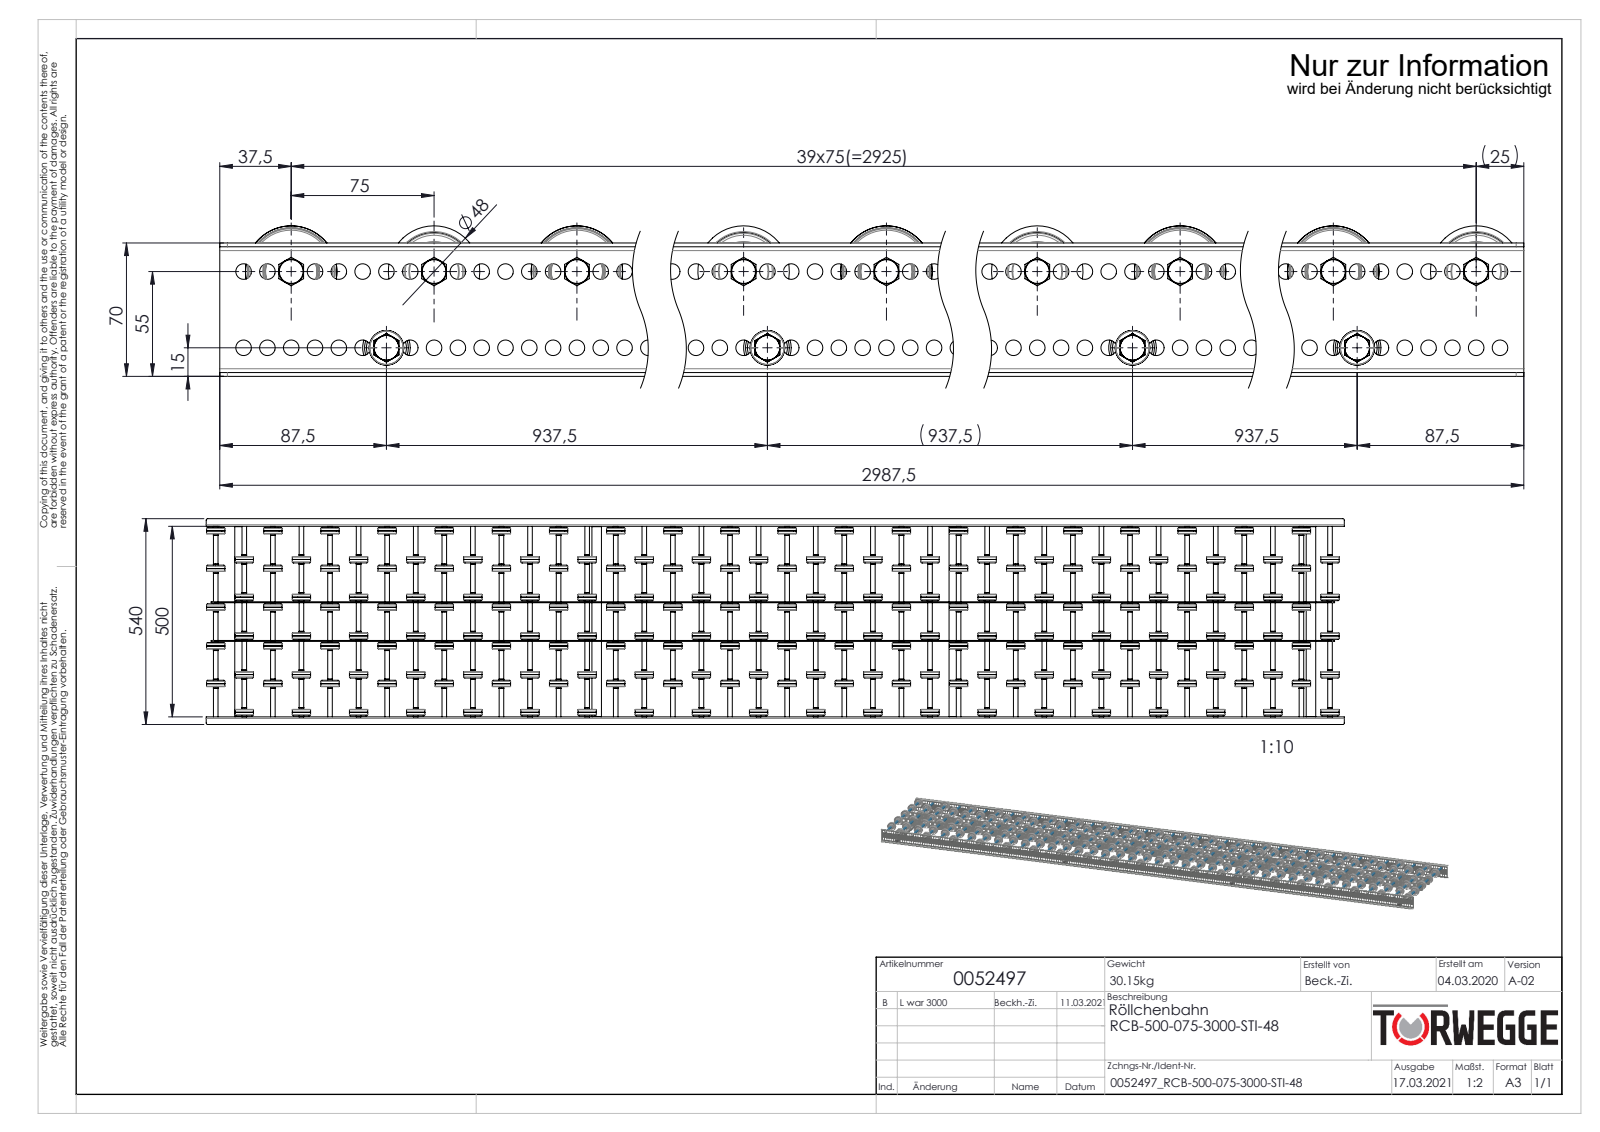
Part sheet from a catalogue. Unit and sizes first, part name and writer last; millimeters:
Units: millimetres
Overall size (bounding box): 2987.5 × 540 × 79
Round holes (diameter × count): ⌀8.2 ×476, ⌀8.5 ×118, ⌀6.65 ×40, ⌀8 ×40, ⌀9.65 ×40, ⌀15 ×40, ⌀41 ×40, ⌀6.8 ×4, ⌀21 ×4
Round bosses / shafts (diameter × count): ⌀48 ×40, ⌀13 ×40, ⌀12.5 ×40, ⌀12.4 ×40, ⌀12 ×40, ⌀11.5 ×40, ⌀25 ×4, ⌀8 ×4
Partial cylindrical surfaces — rounded edges, fillets, slot ends (radius × count): R4 ×8, R2 ×4, R5 ×4
Main face-to-face distances: 200.5, 302, 101.5, 2, 12, 87, 99, 75, 502, 186
Hole centre spacings: 12.5, 25, 37.5, 50, 62.5, 75, 87.5, 100
Volume: 7 988 000 mm³ · Surface area: 6 125 000 mm²
Bodies: 744 solids, 22664 faces (4536 planar, 8880 cylindrical, 9248 other)
Part name (STEP PRODUCT): K0011528_2200-48-8; 0046278_KB-ROHR-12X1,75mm_KFG_L75; Hutmutter_DIN_1587_M8; S106837_Gewindestange-M8-KFG_L520 (+6 more)
STEP written by: SolidWorks 2020 (AUTOMOTIVE_DESIGN)
